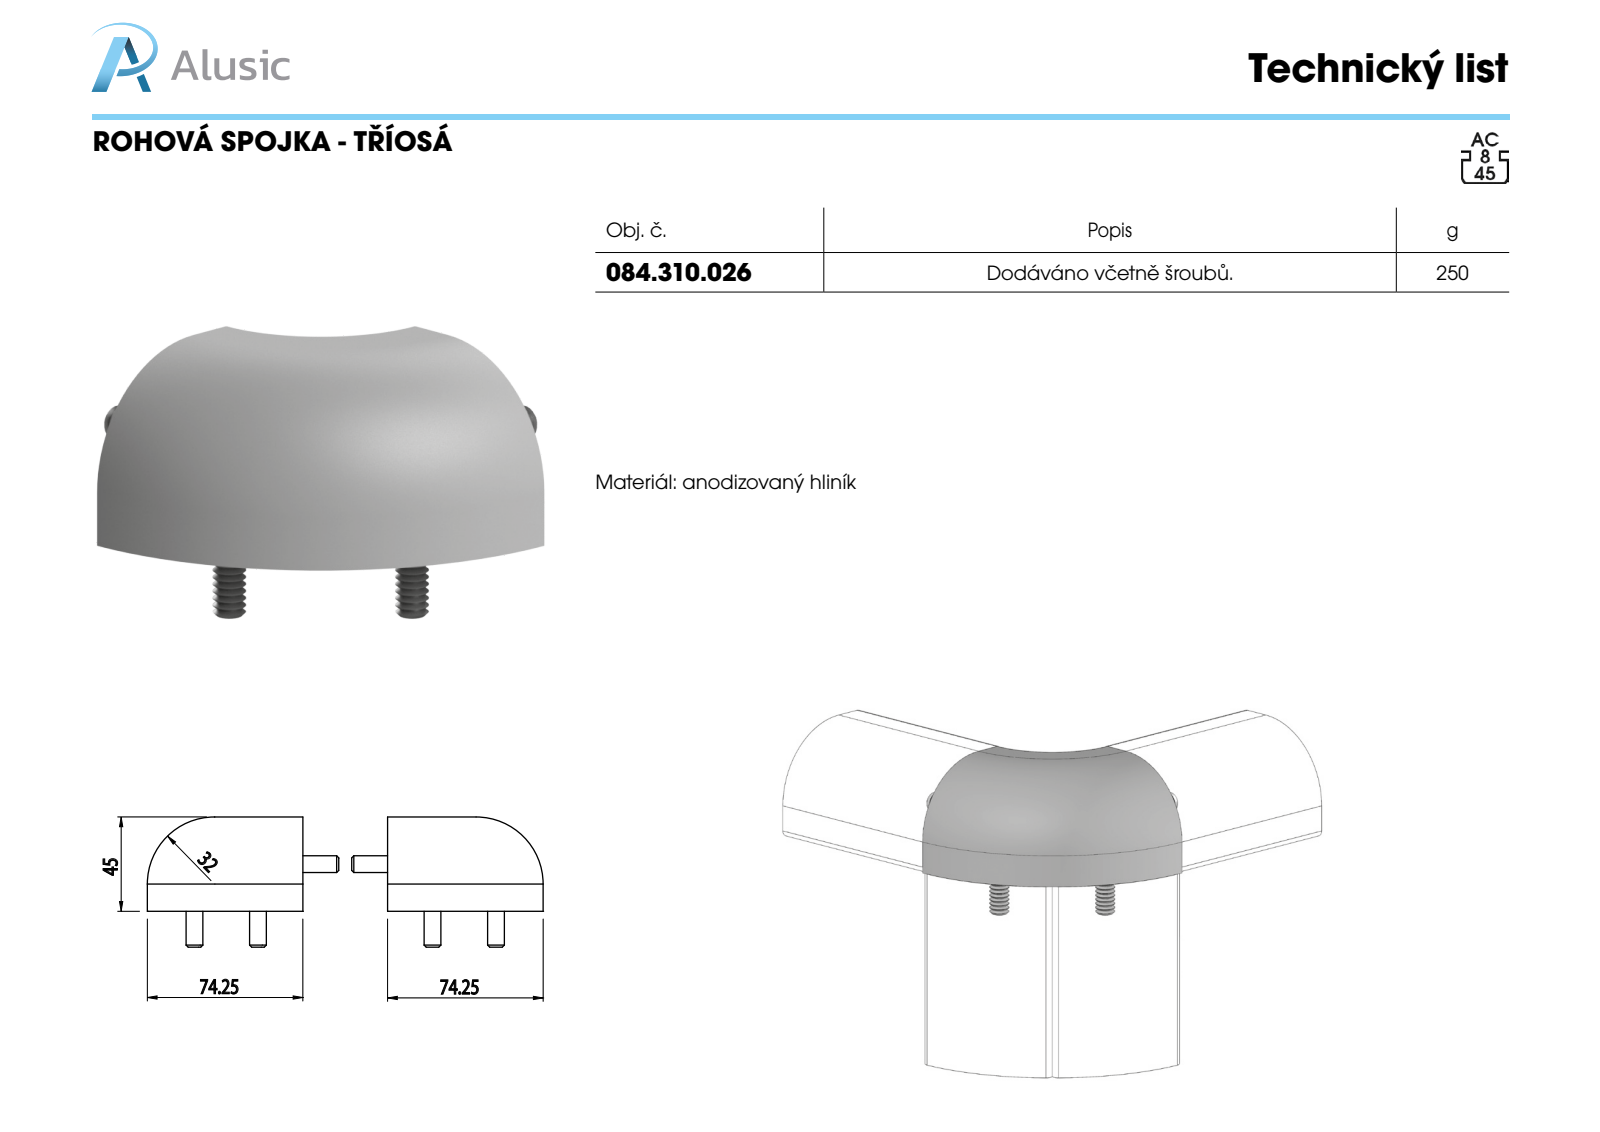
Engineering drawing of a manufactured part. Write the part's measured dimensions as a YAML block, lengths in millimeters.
part_name: "084.310.026L_Default<A macchina>; 084.310.026; GRANI A PUNTA CONICA UNI 5927_M8x20 UNI 5927; 203208"
step_written_by: "SolidWorks 2016 (CONFIG_CONTROL_DESIGN)"
units: millimeters
bodies: {solids: 9, faces: 164, planar: 48, cylindrical: 50, other: 66}
overall_size: [90.75, 90.75, 61.5]
volume: 140933
surface_area: 27049
round_holes:
  - {diameter: 6.8, count: 4}
  - {diameter: 8.2, count: 4}
round_bosses_or_shafts:
  - {diameter: 8, count: 8}
partial_cylinders:
  - {radius: 29.25, count: 1}
  - {radius: 74.25, count: 1}
face_to_face_distances: [45, 15.5, 16.5, 32, 29.5, 4, 61.5, 3.2, 45.36, 28.86]
hole_center_spacings: [42.25, 42.86]
